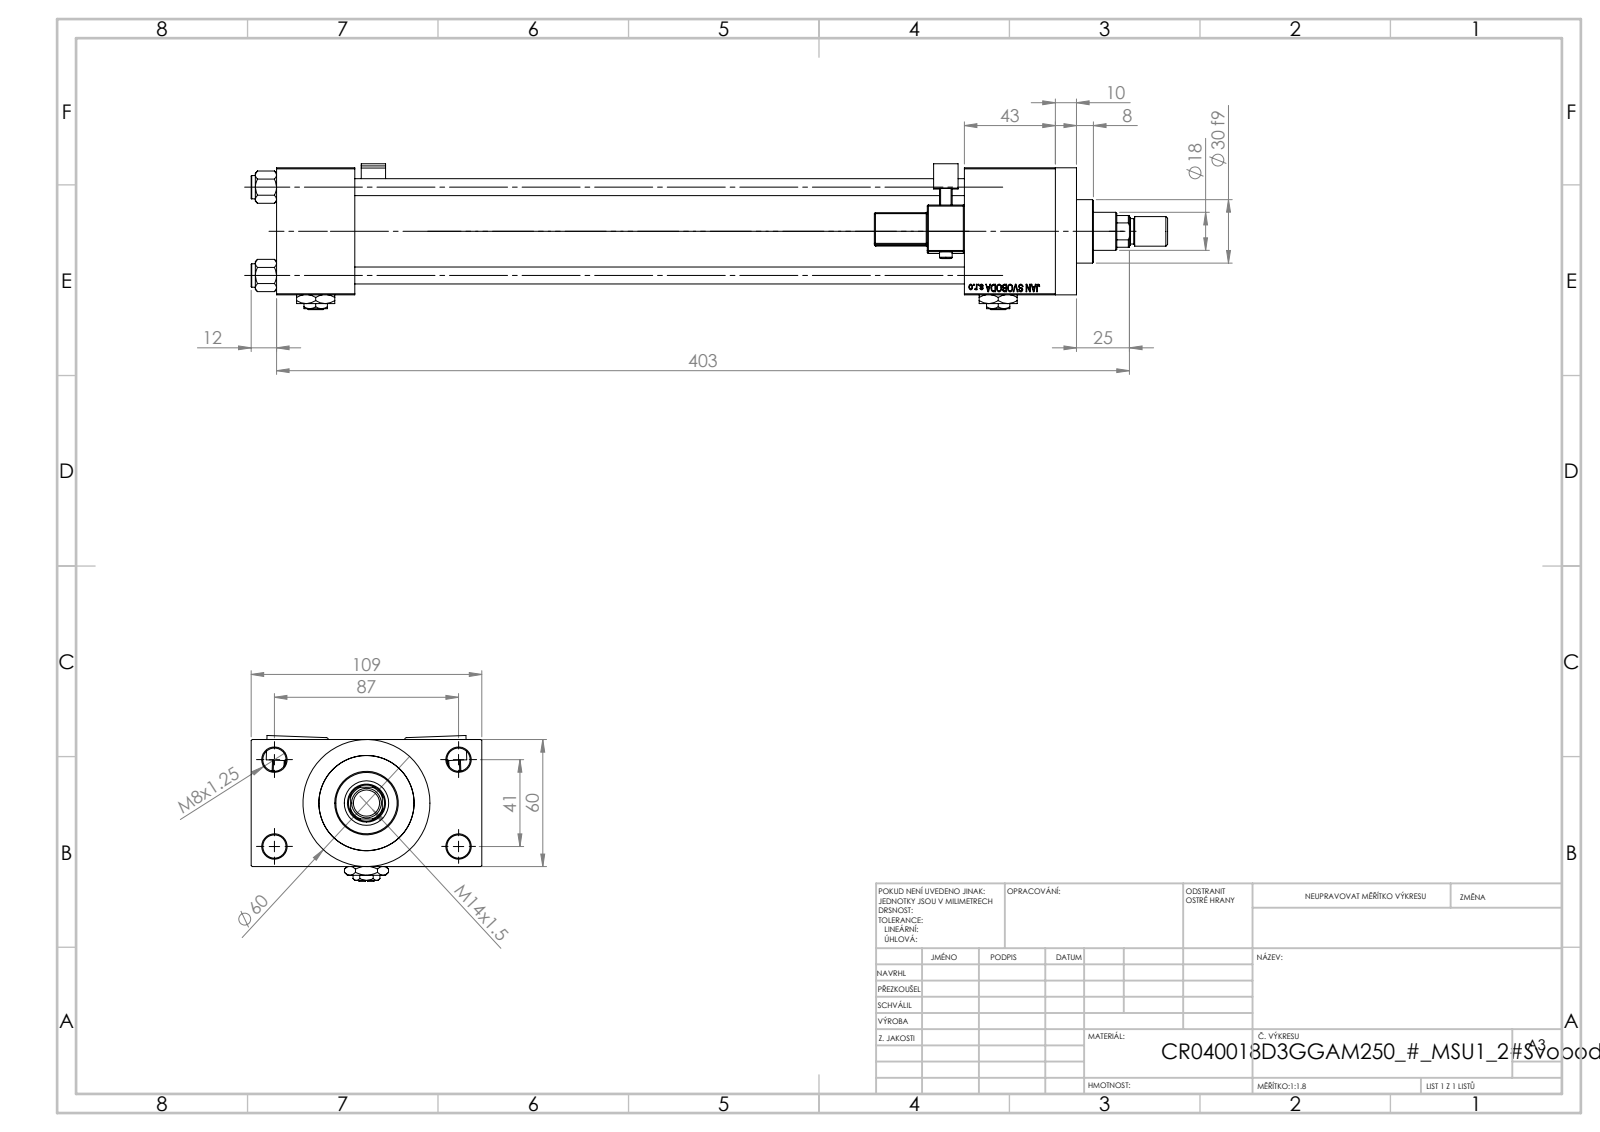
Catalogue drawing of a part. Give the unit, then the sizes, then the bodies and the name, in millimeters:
Units: millimetres
Overall size (bounding box): 433 × 109 × 68.9
Round holes (diameter × count): ⌀8 ×4, ⌀11 ×4, ⌀7 ×2, ⌀16.66 ×2, ⌀24 ×2, ⌀8.5 ×1, ⌀18 ×1, ⌀21 ×1, ⌀31 ×1, ⌀40 ×1, ⌀45 ×1
Round bosses / shafts (diameter × count): ⌀11 ×4, ⌀6 ×2, ⌀60 ×1, ⌀46 ×1, ⌀30 ×1, ⌀14 ×1, ⌀12 ×1
Partial cylindrical surfaces — rounded edges, fillets, slot ends (radius × count): R0.5 ×48, R1 ×2, R2.5 ×2, R4 ×2, R8.5 ×1
Main face-to-face distances: 60, 288, 24.5, 84.5, 37, 325, 43, 368, 331, 109
Hole centre spacings: 22.65, 29.49, 41.7, 47.15, 48.09, 64.35, 76.49, 41
Volume: 757 083 mm³ · Surface area: 235 397 mm²
Bodies: 16 solids, 1374 faces (608 planar, 164 cylindrical, 602 other)
Part name (STEP PRODUCT): NUT_M5_D; V215CR_D_Body; V215CR_VCP_D; V215CR_D_TYCINKA (+4 more)
STEP written by: SolidWorks 2019 (CONFIG_CONTROL_DESIGN)
